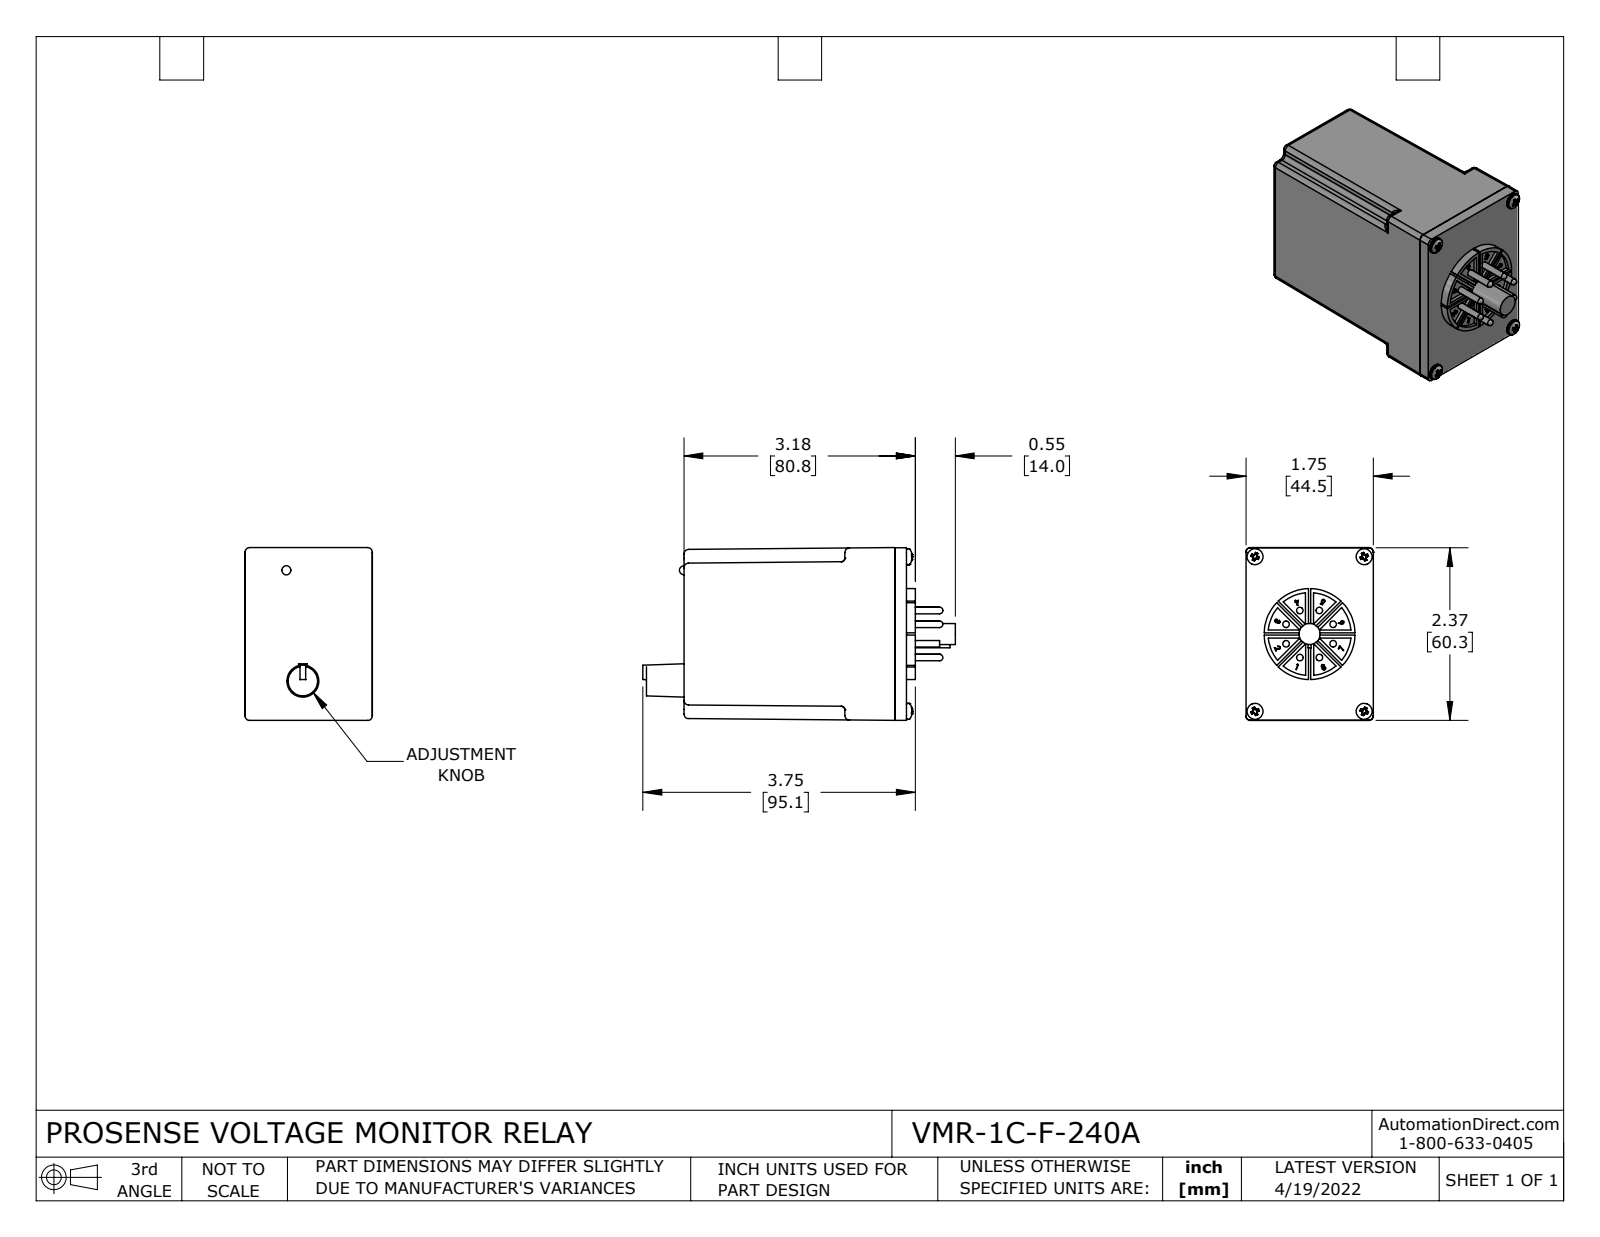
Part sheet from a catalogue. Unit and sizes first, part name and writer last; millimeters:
Units: millimetres
Overall size (bounding box): 109.1 × 60.3 × 44.5
Round holes (diameter × count): ⌀3.2 ×4
Round bosses / shafts (diameter × count): ⌀2.3 ×8, ⌀5.6 ×4, ⌀31.8 ×1, ⌀7.4 ×1
Partial cylindrical surfaces — rounded edges, fillets, slot ends (radius × count): R1.6 ×32, R0.1 ×8, R1.3 ×4, R14.5 ×1
Main face-to-face distances: 73.7, 4.1, 77.7, 1.8, 5.8, 79.5, 4.8, 1.3, 3, 7.1
Hole centre spacings: 38.1, 54, 66.1
Volume: 202 100 mm³ · Surface area: 29 540 mm²
Bodies: 17 solids, 542 faces (221 planar, 164 cylindrical, 157 other)
Part name (STEP PRODUCT): VMR-1C-F-240A
STEP written by: SolidWorks 2021 (CONFIG_CONTROL_DESIGN)
